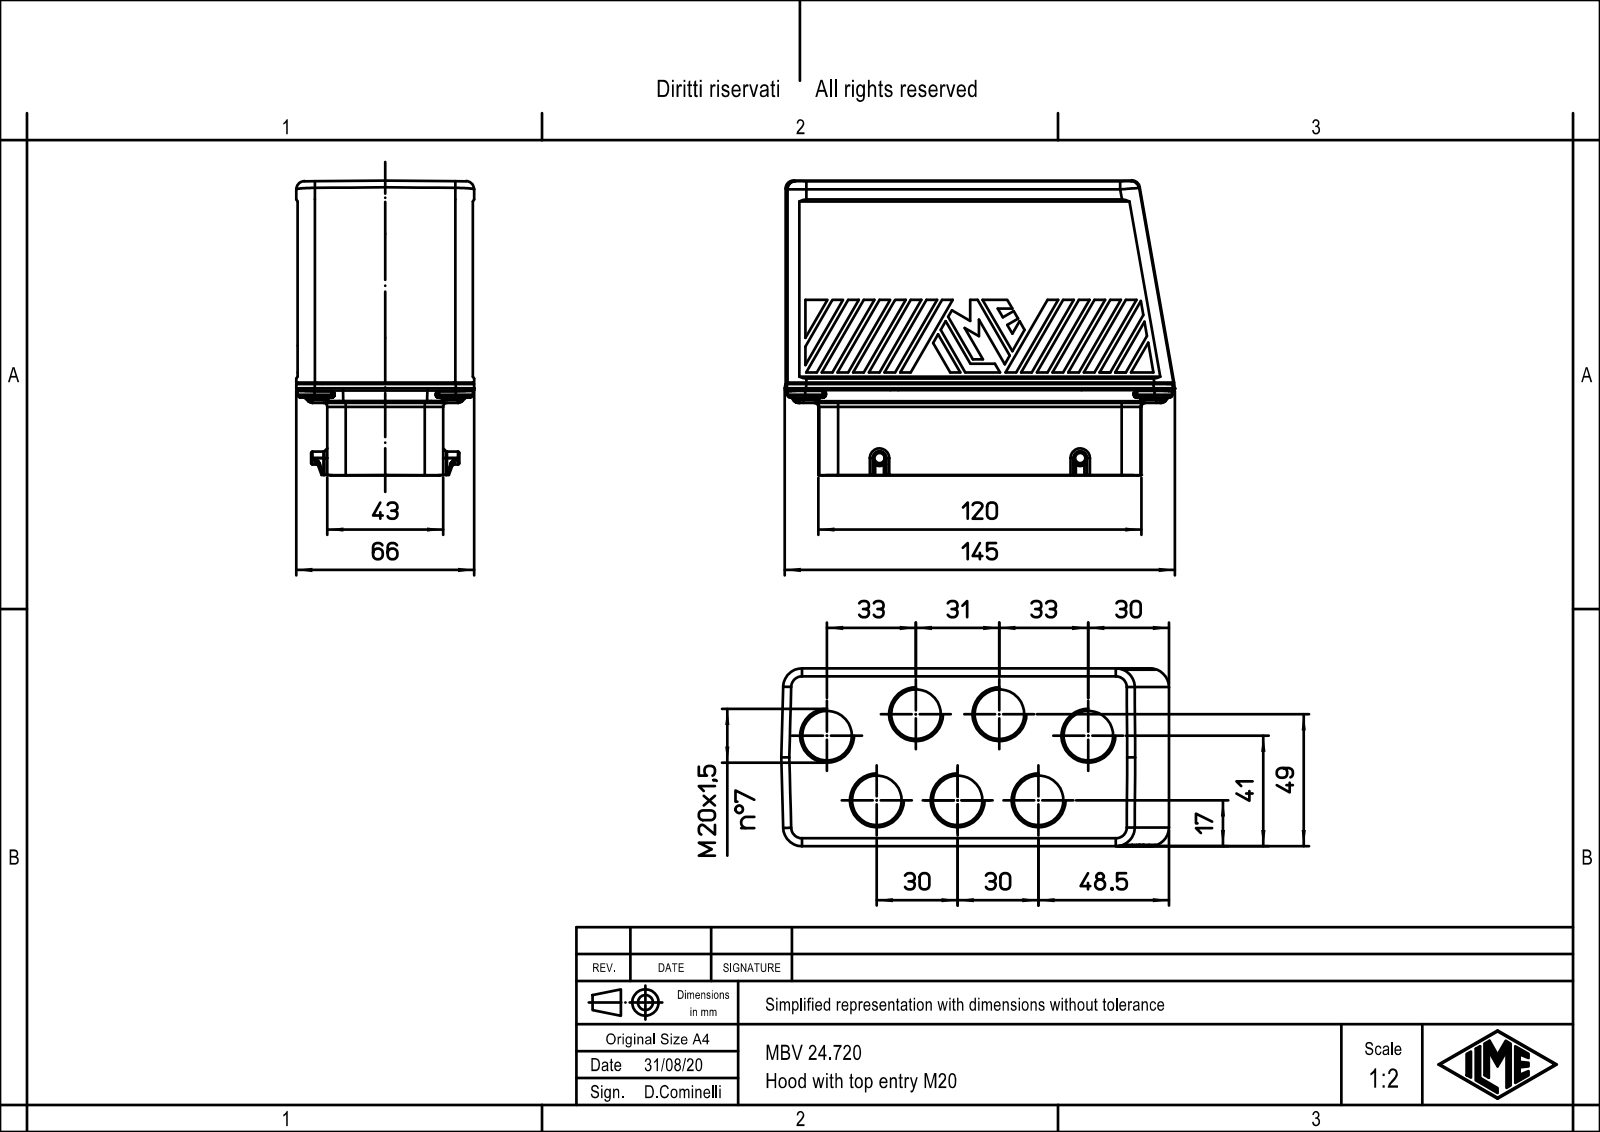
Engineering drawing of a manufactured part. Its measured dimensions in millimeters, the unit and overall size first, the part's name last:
Units: millimetres
Overall size (bounding box): 143.75 × 108.97 × 66.01
Round holes (diameter × count): ⌀20 ×7
Round bosses / shafts (diameter × count): ⌀4.8 ×2
Partial cylindrical surfaces — rounded edges, fillets, slot ends (radius × count): R1 ×34, R7 ×12, R0.5 ×8, R1.5 ×6, R3 ×6, R4.2 ×4, R5 ×4, R6.5 ×4
Main face-to-face distances: 65.01, 82.21, 0.4, 65.41, 11, 54.01, 54, 43, 11.01, 52.21
Hole centre spacings: 30, 35.13, 35.56, 55.63, 30.24, 30.3, 31, 33.86
Volume: 691 716 mm³ · Surface area: 80 140 mm²
Bodies: 1 solid, 568 faces (370 planar, 112 cylindrical, 86 other)
Part name (STEP PRODUCT): MBV_24.720
STEP written by: Creo Elements/Direct Modeling 20.1B 02-Apr-2019 (C) Parametric Technology GmbH (AUTOMOTIVE_DESIGN)
